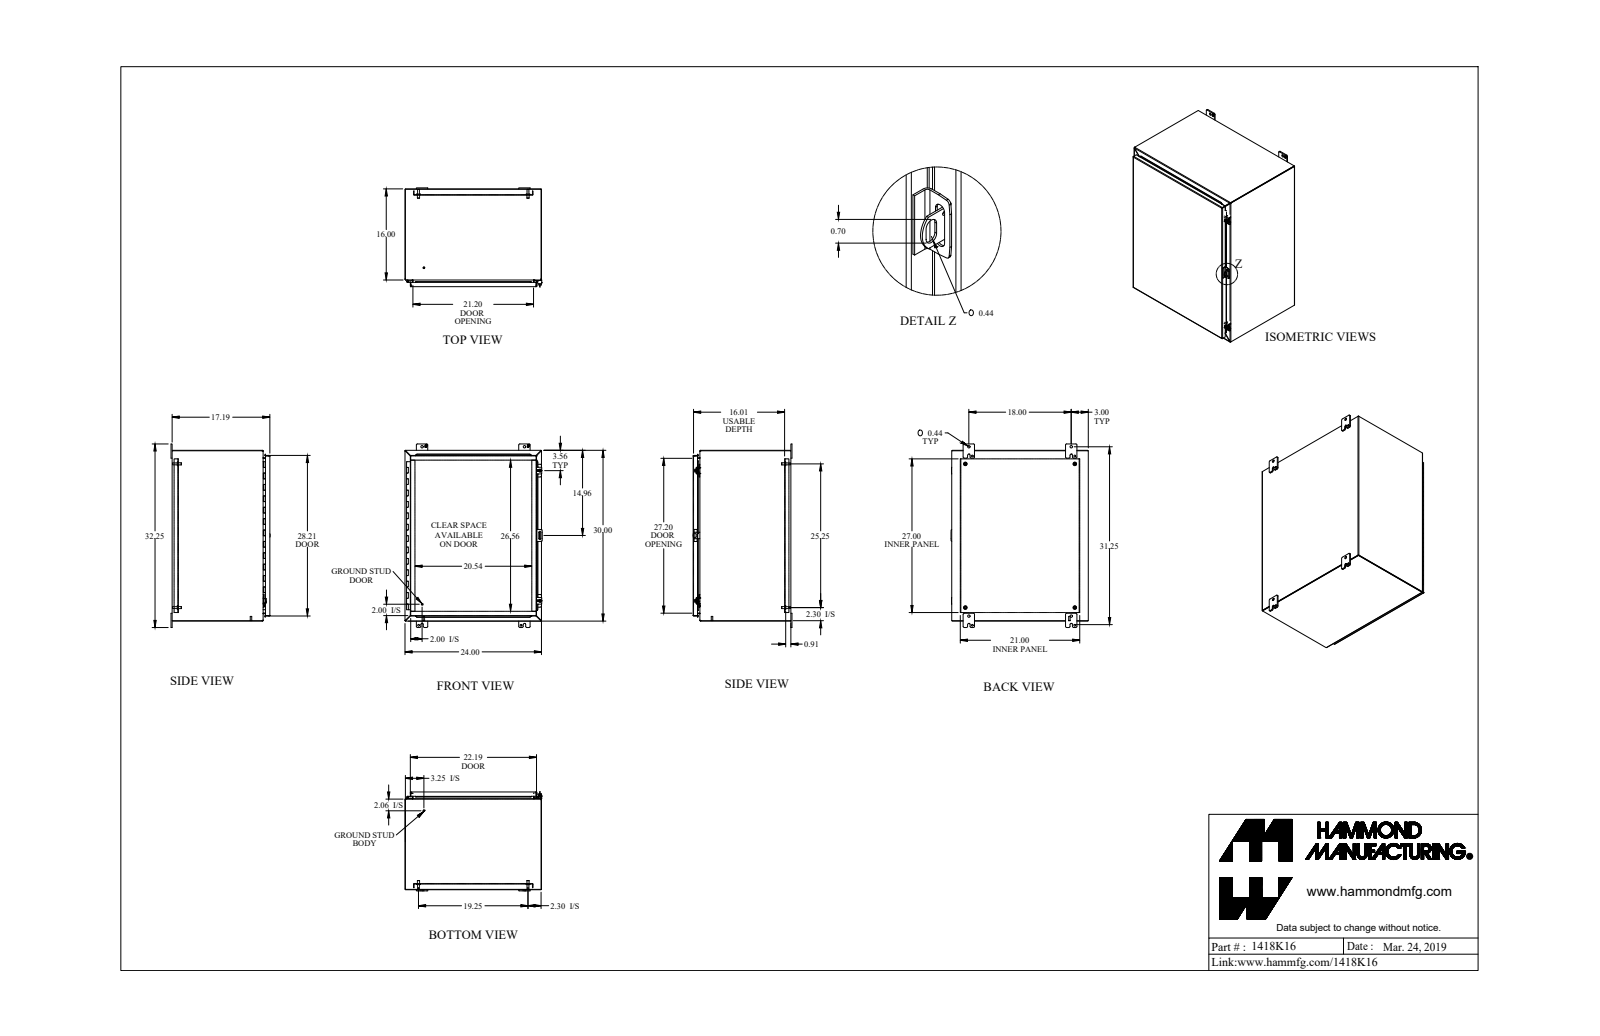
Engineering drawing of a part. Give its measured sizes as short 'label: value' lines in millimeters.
name: 1418K16_Default
written by: SolidWorks 2019 (CONFIG_CONTROL_DESIGN)
unit: mm
bodies: 40 solids, 1203 faces (723 planar, 404 cylindrical, 76 other)
size: 819.2 × 612.8 × 442.9
volume: 5 329 000 mm³; area: 5 511 000 mm²
holes: 4× ⌀8, 4× ⌀11.1, 4× ⌀12.7, 2× ⌀5.4, 2× ⌀6.7, 2× ⌀7.8, 2× ⌀9.5, 1× ⌀3.2, 1× ⌀4.7, 1× ⌀11.3, 1× ⌀11.3
bosses: 4× ⌀16.5, 4× ⌀9.5, 4× ⌀8.4, 2× ⌀25.4, 2× ⌀12.7, 2× ⌀9.9, 2× ⌀7.1, 2× ⌀6.4
rounds: 26× R4.8, 22× R0.9, 22× R2.7, 13× R1.2, 13× R3.6, 12× R6.4, 8× R1, 8× R5.5
face distances: 1.8, 434.7, 607.8, 760.2, 432.8, 436.5, 23.8, 2.4, 25.6, 408.5
hole spacings: 44.1, 457.2, 755.7, 883.2, 489, 806.5, 41.3, 61.8
